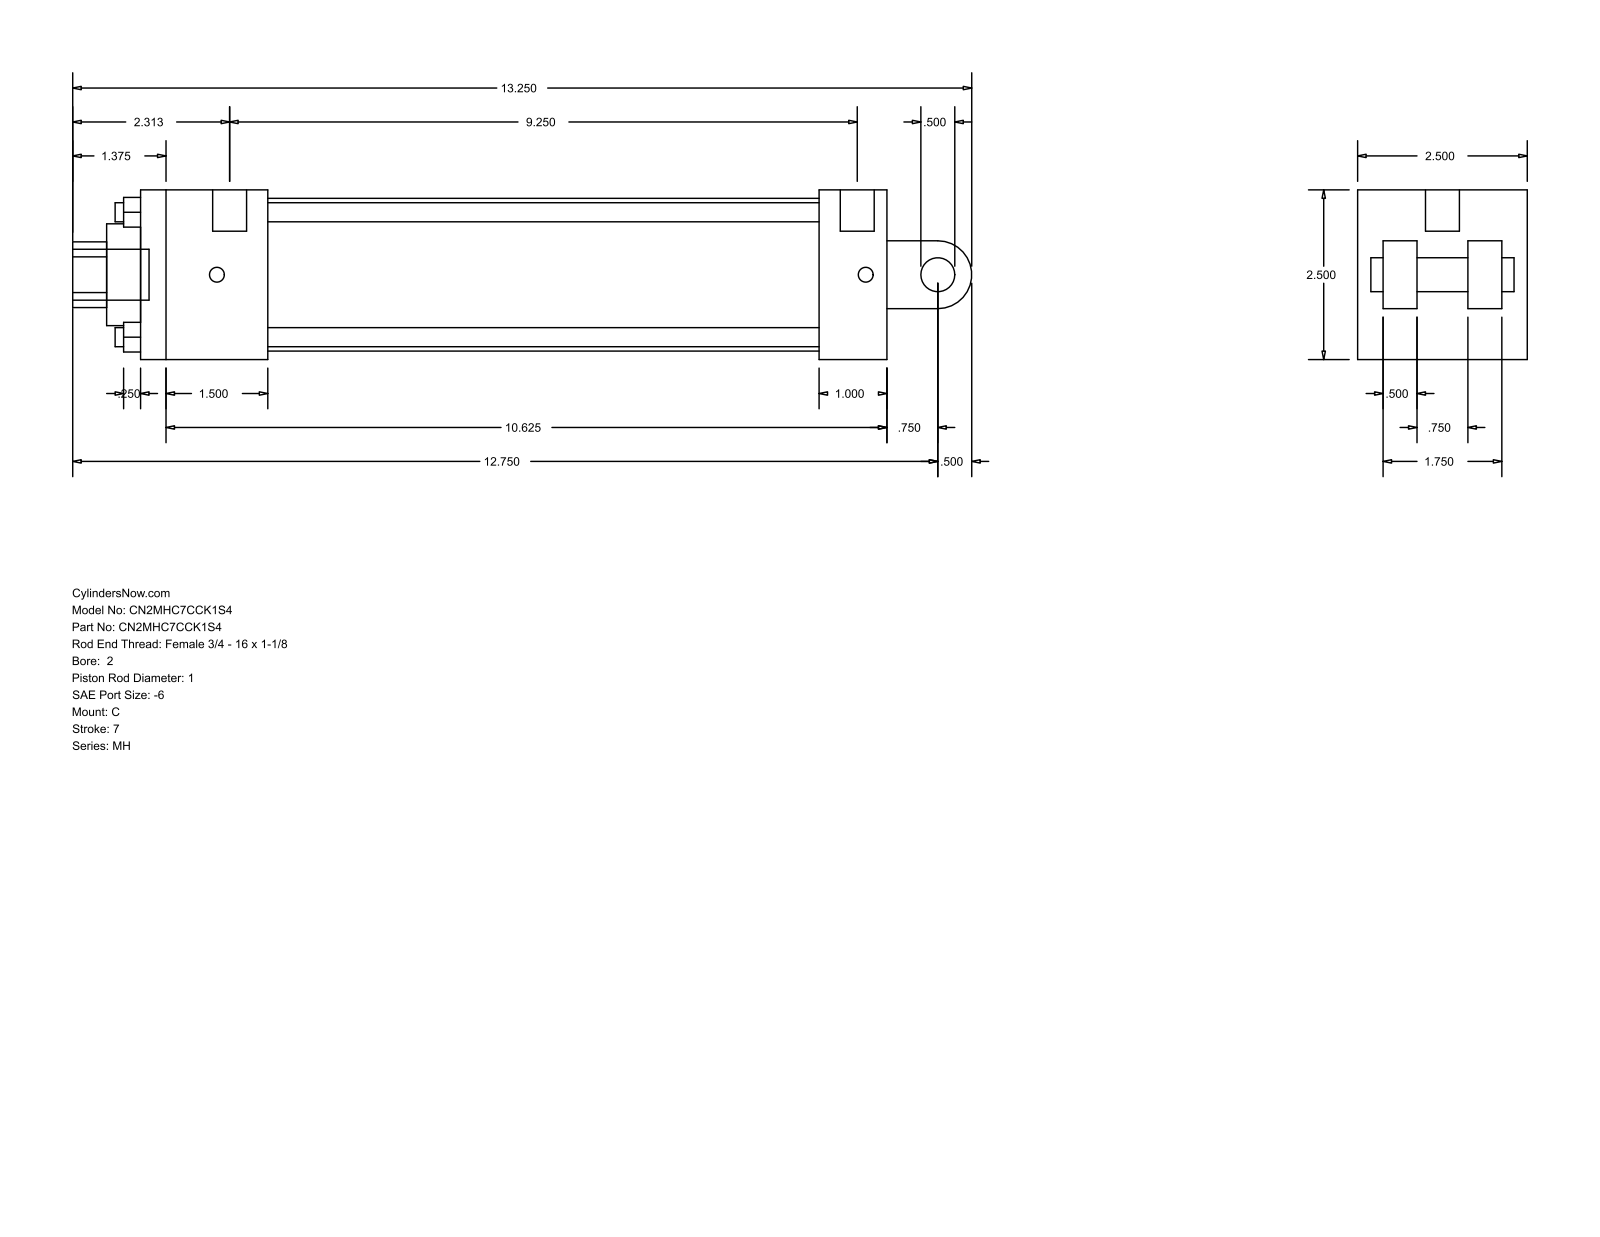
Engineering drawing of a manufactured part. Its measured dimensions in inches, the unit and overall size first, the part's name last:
Units: inches
Overall size (bounding box): 13.25 × 2.5 × 2.5
Round holes (diameter × count): ⌀0.281 ×4, ⌀0.219 ×2, ⌀0.5 ×1, ⌀1 ×1, ⌀1.5 ×1, ⌀2.25 ×1
Round bosses / shafts (diameter × count): ⌀0.5 ×2, ⌀0.219 ×2, ⌀0.75 ×1
Partial cylindrical surfaces — rounded edges, fillets, slot ends (radius × count): R0.484 ×1, R0.5 ×1
Main face-to-face distances: 2.5, 11, 0.5, 1, 0.375, 1.875, 2.125, 10, 8.125, 9.125
Hole centre spacings: 1.301, 1.84, 2.602, 0.125
Bodies: 0 solids, 99 faces (70 planar, 29 cylindrical, 0 other)
Part name (STEP PRODUCT): MH_C__0200_1
STEP written by: GSSL Pune (CONFIG_CONTROL_DESIGN)
